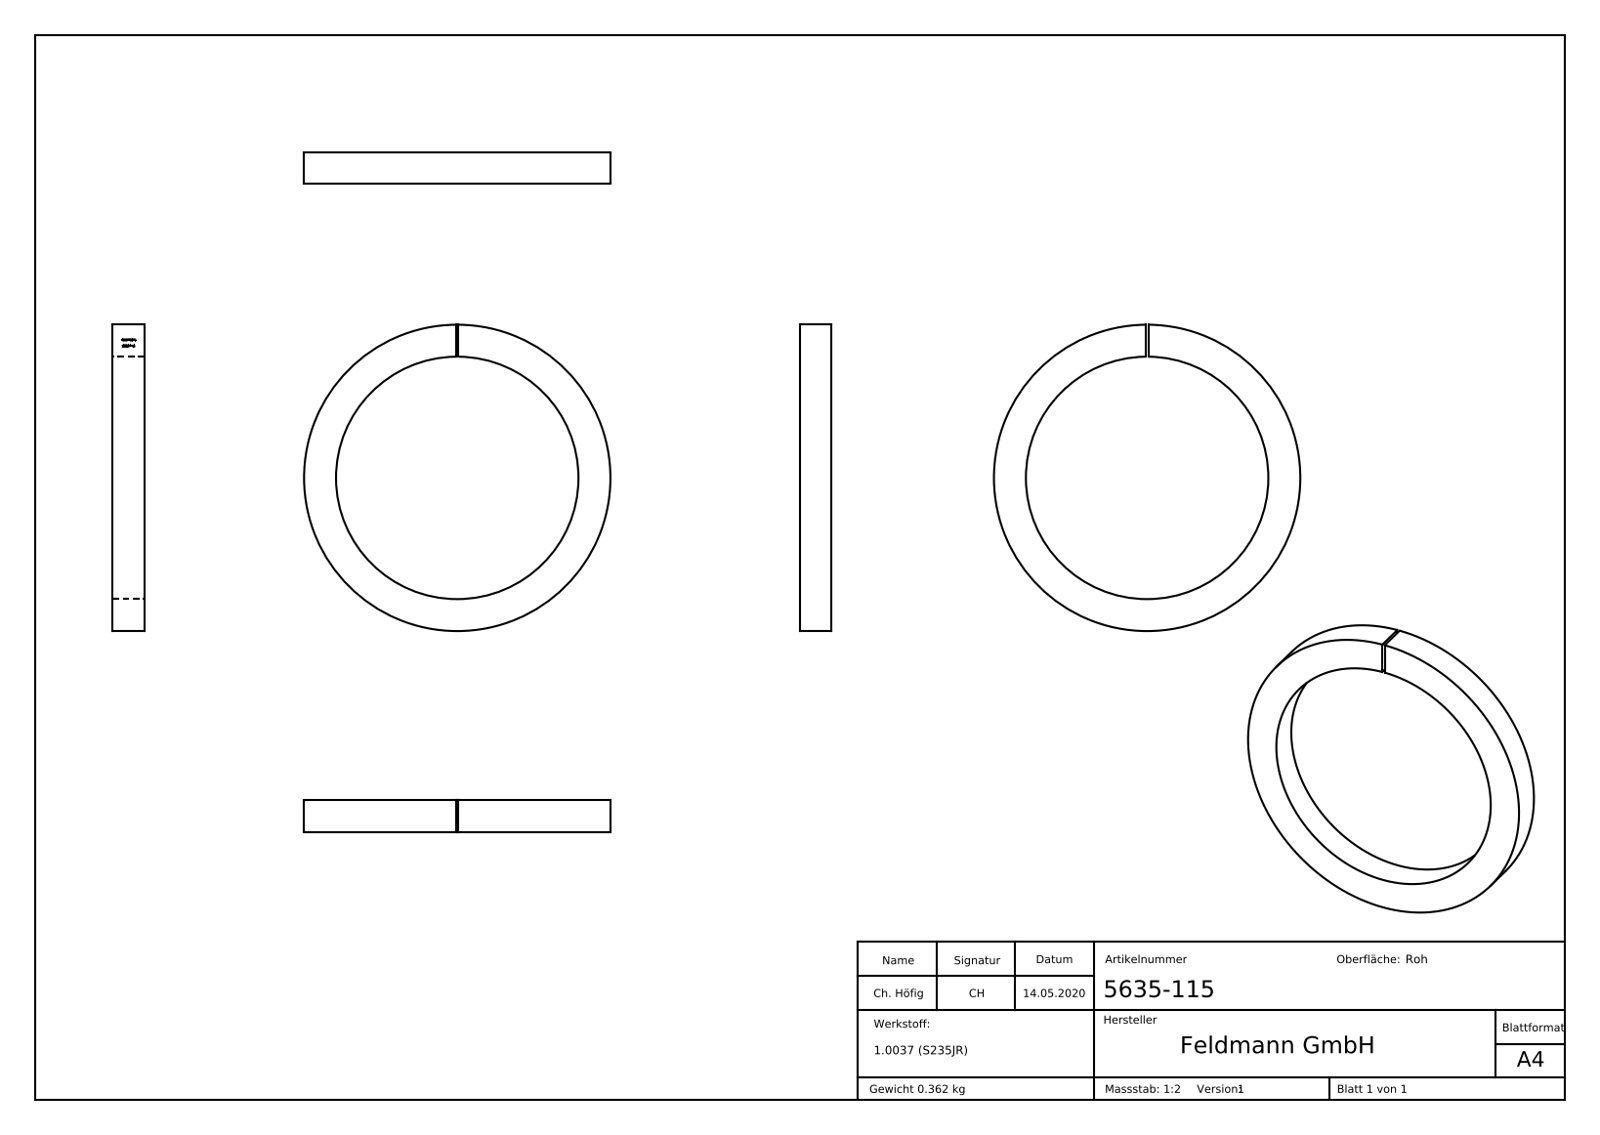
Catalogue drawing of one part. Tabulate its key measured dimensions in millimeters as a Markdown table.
| quantity | value |
| --- | --- |
| part name | 5635-115 |
| STEP written by | SolidWorks 2015 (CONFIG_CONTROL_DESIGN) |
| units | millimeters |
| bodies | 1 solid, 215 faces (118 planar, 2 cylindrical, 95 other) |
| overall size | 115 × 115 × 12 |
| volume | 46 452 mm³ |
| surface area | 15 777 mm² |
| round holes (diameter × count) | 91 × 1 |
| round bosses / shafts (diameter × count) | 115 × 1 |
| main face-to-face distances | 12, 1, 1.1, 1.78, 2.12, 0.83, 1.98, 2.77, 1.21, 3.33 |
